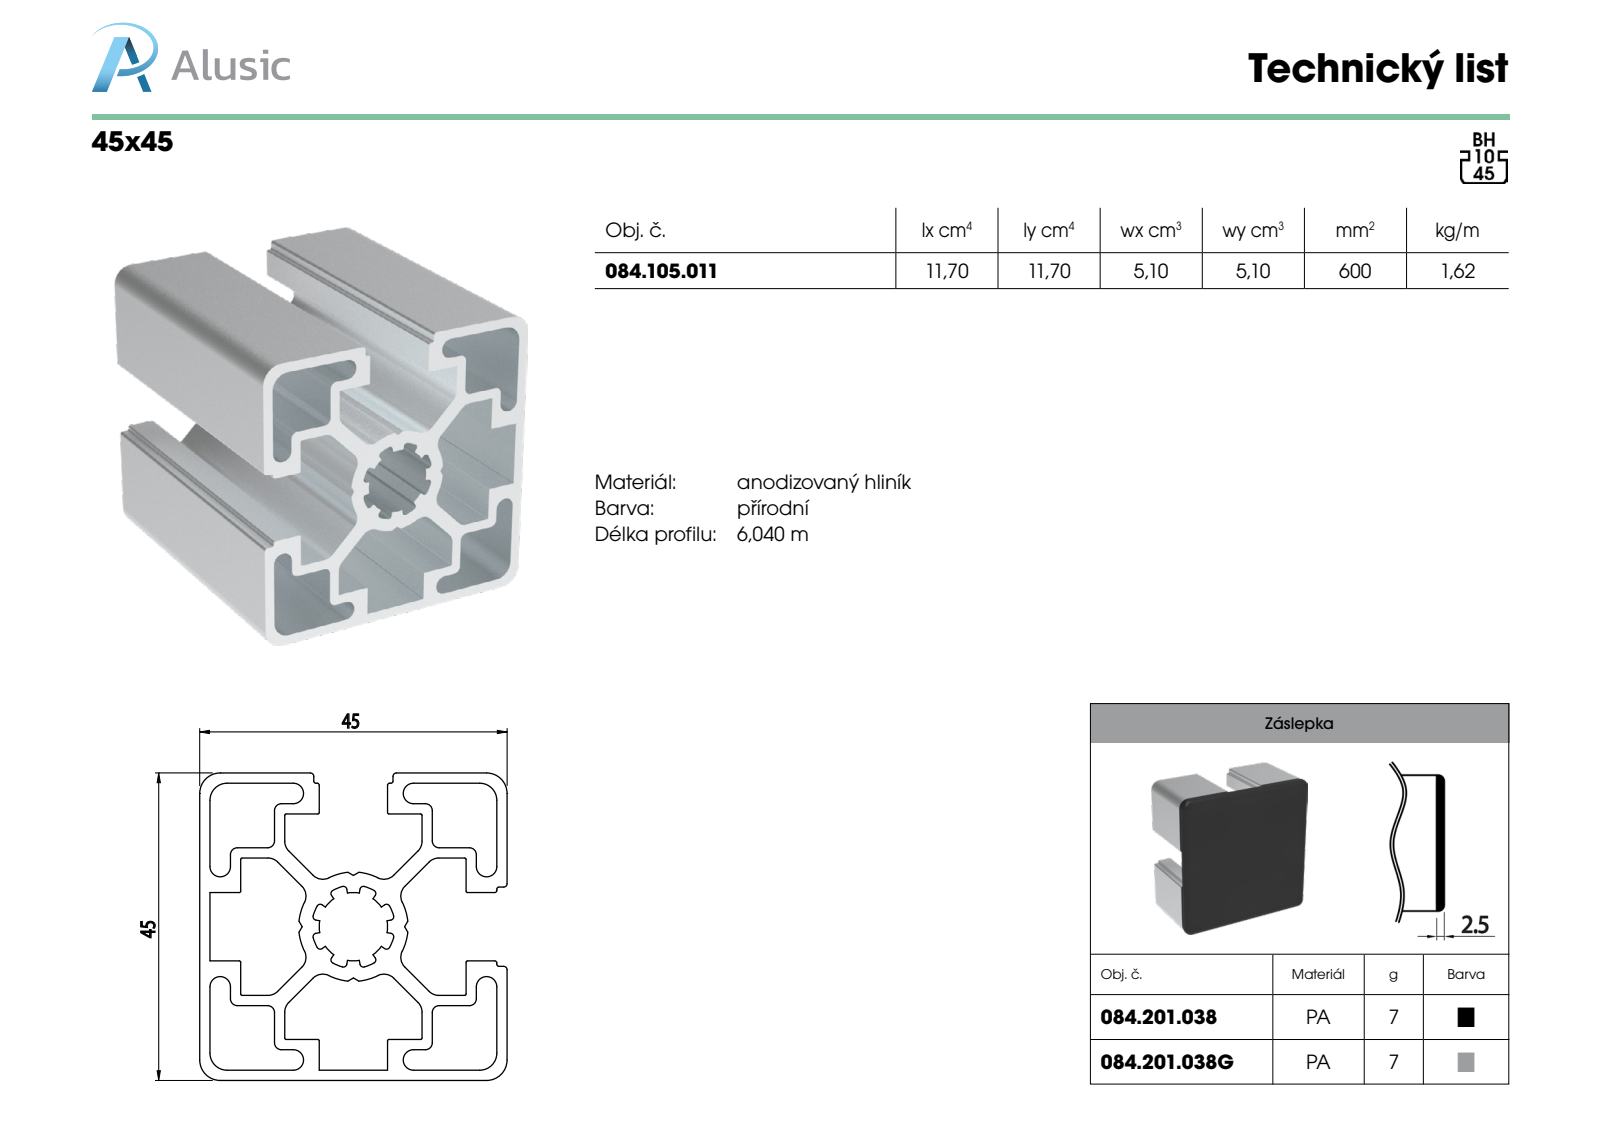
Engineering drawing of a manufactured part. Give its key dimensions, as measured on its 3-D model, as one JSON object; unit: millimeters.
{"part_name": "084.105.011", "step_written_by": "SolidWorks 2018 (AUTOMOTIVE_DESIGN)", "units": "millimeters", "bodies": {"solids": 1, "faces": 219, "planar": 98, "cylindrical": 121, "other": 0}, "overall_size": [100, 45, 45], "volume_mm3": 60021, "surface_area_mm2": 65012, "partial_cylinders_radius": [[0.5, 20], [0.2, 16], [2, 16], [1, 12], [0.3, 8], [1.5, 8], [2.5, 4], [3, 4]], "face_to_face_distances": [1.5, 43.5, 10.95, 32.55, 45, 39, 4.5, 28.05, 6.45, 42]}
